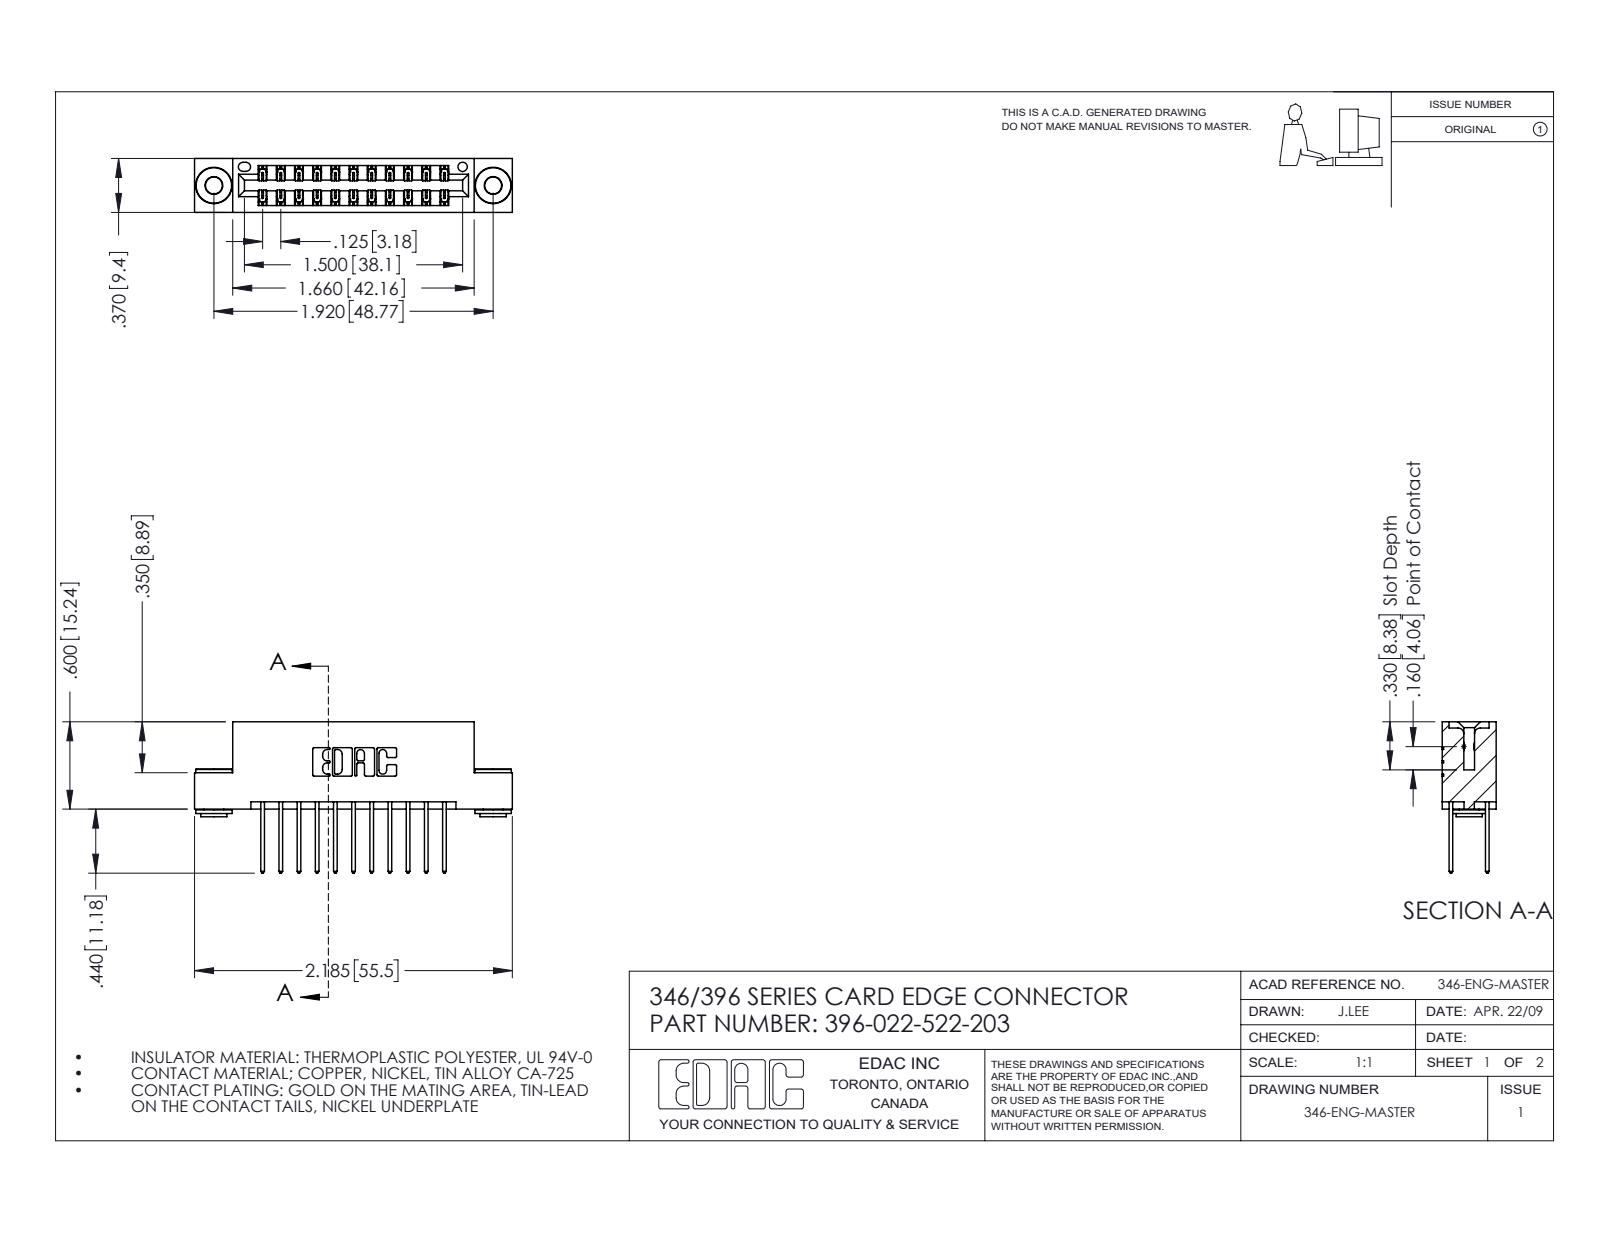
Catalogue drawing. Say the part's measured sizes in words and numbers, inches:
The part is named "345-292-001_345-293-122; 345-250-002_345-250-002-102; 346 Part_Flush Mounting Lugs - 0.156 Dia-TH; 396-022-522-203". Its 3-D file was written by "SolidWorks 2016 (CONFIG_CONTROL_DESIGN)". It is 25 solids with 1304 faces: 856 planar, 440 cylindrical and 8 other. Overall it measures 2.185 by 1.04 by 0.37 inches. Its volume is 0.32 cubic inches and its surface area 11.16 square inches. Round holes: 2 of diameter 0.116, 2 of diameter 0.156, 1 of diameter 0.064. Round bosses or shafts: 2 of diameter 0.25, 2 of diameter 0.18, 2 of diameter 0.136. Partial cylindrical surfaces (rounded edges, fillets, slot ends): 33 of radius 0.006, 22 of radius 0.01, 22 of radius 0.01, 6 of radius 0.007, 6 of radius 0.031, 3 of radius 0.026, 2 of radius 0.014, 2 of radius 0.022. The main face-to-face distances are 0.25, 0.048, 0.322, 0.37, 0.025, 0.072, 0.298, 0.275, 0.148, 0.222. The hole center spacings are 0.246, 1.715, 1.92.
